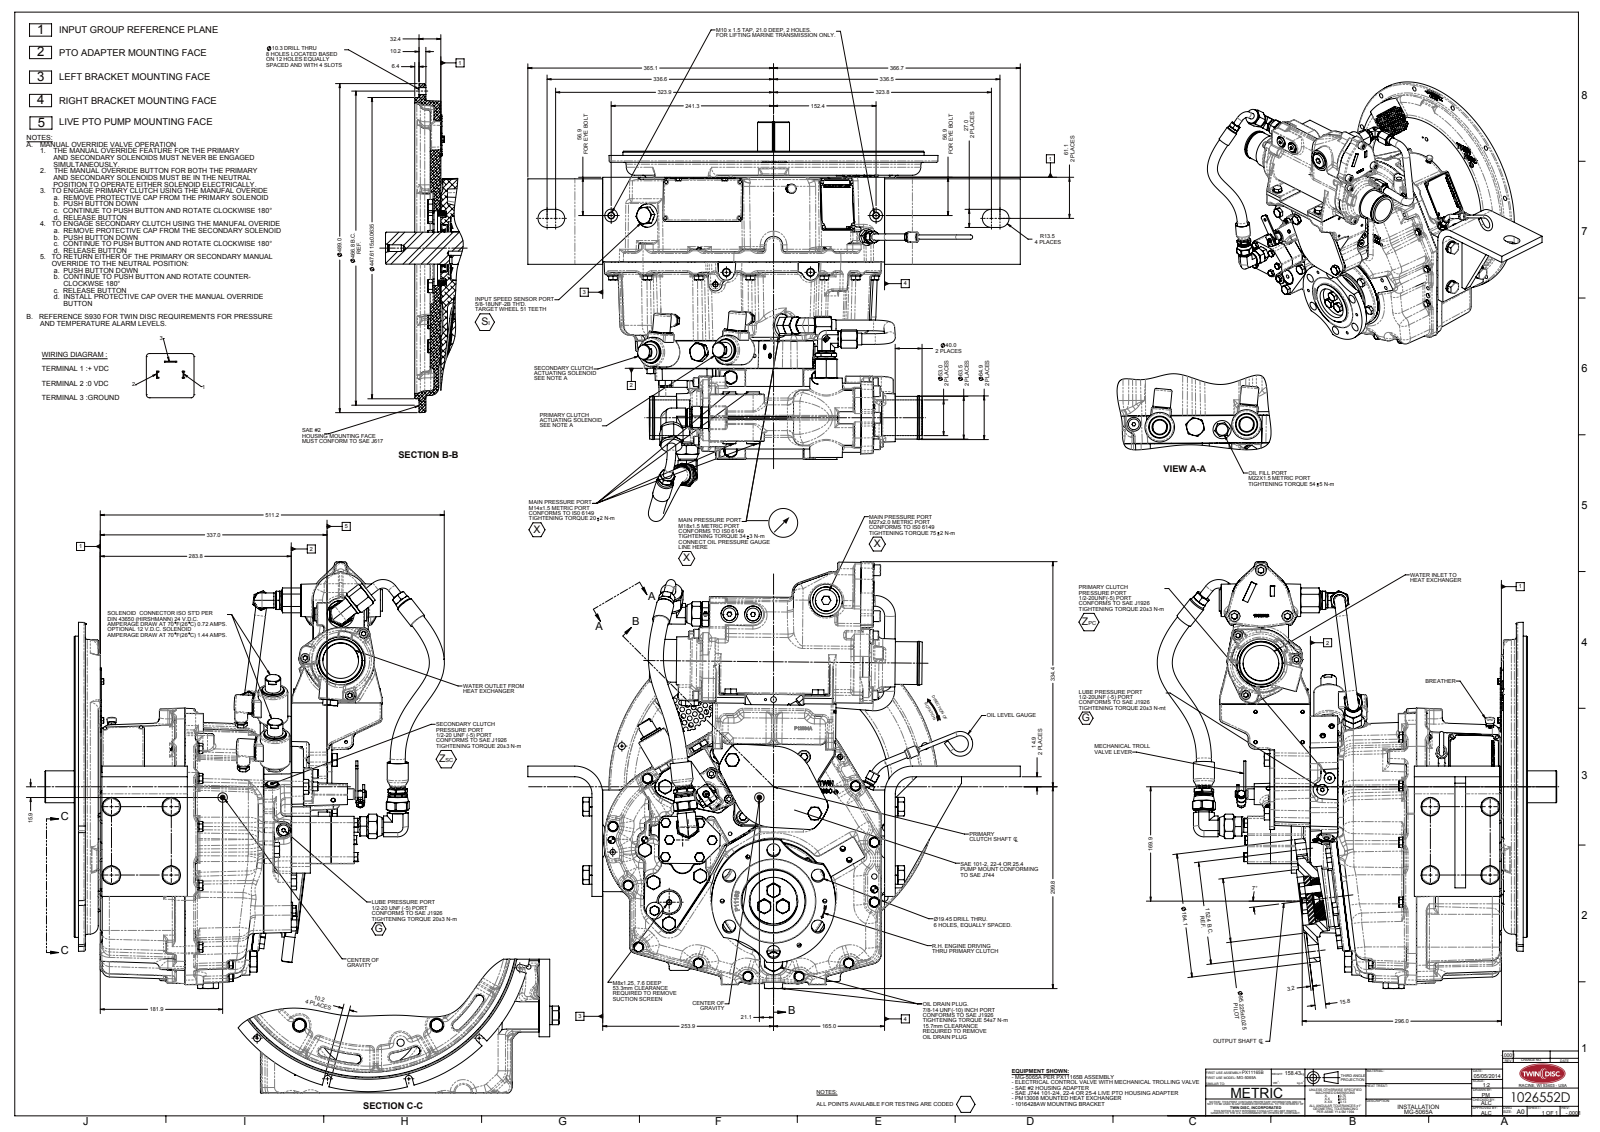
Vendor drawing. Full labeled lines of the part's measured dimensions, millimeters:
Part name (STEP PRODUCT): 1026552D
STEP written by: SolidWorks 2010 (AUTOMOTIVE_DESIGN)
Units: millimetres
Bodies: 0 solids, 10429 faces (5454 planar, 2245 cylindrical, 2730 other)
Overall size (bounding box): 731.84 × 634.3 × 593.71
Round holes (diameter × count): ⌀7 ×54, ⌀8 ×10, ⌀10.32 ×8, ⌀19.45 ×6, ⌀10 ×5, ⌀5 ×4, ⌀6 ×4, ⌀10.72 ×4, ⌀12 ×4, ⌀19 ×4, ⌀25 ×3, ⌀4.6 ×2
Round bosses / shafts (diameter × count): ⌀15.88 ×14, ⌀21 ×11, ⌀13 ×11, ⌀19 ×5, ⌀27.4 ×4, ⌀19.85 ×4, ⌀15.87 ×4, ⌀16 ×3
Partial cylindrical surfaces — rounded edges, fillets, slot ends (radius × count): R16.96 ×168, R1.27 ×160, R0.8 ×109, R1 ×89, R4 ×74, R3.05 ×73, R2 ×52, R8 ×46
Main face-to-face distances: 15.75, 126.29, 142.04, 10.16, 123.41, 2.88, 18.63, 240.36, 0.41, 123
Hole centre spacings: 76.2, 10, 20, 30, 233.35, 17.34, 10.03, 26.47
